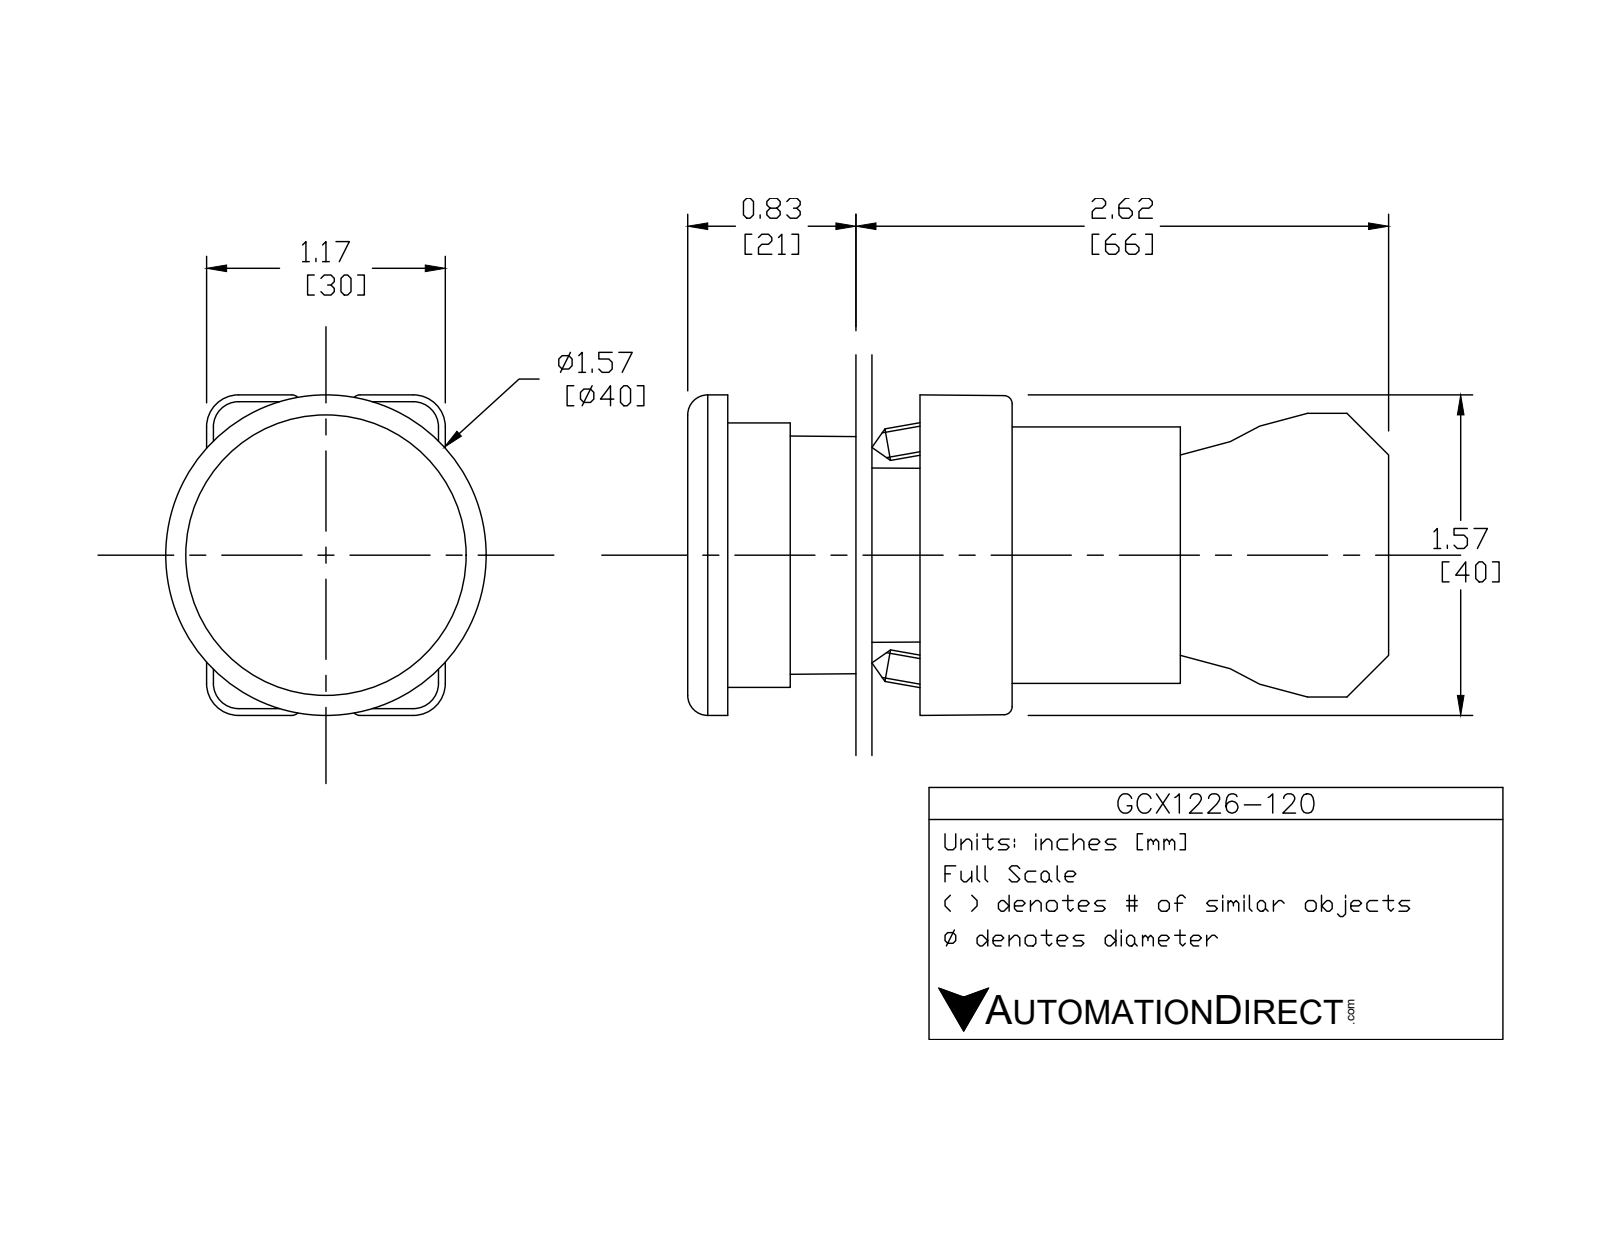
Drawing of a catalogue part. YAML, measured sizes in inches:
part_name: "GCX1226-120; ECX1050; ecx1030; GCX122X OPERATOR (+1 more)"
step_written_by: "SolidWorks 2016 (AUTOMOTIVE_DESIGN)"
units: inches
bodies: {solids: 7, faces: 431, planar: 252, cylindrical: 146, other: 33}
overall_size: [3.469, 1.581, 1.575]
volume: 2.895
surface_area: 40.89
round_holes:
  - {diameter: 0.079, count: 2}
  - {diameter: 0.124, count: 2}
  - {diameter: 0.13, count: 2}
  - {diameter: 0.087, count: 1}
  - {diameter: 0.197, count: 1}
  - {diameter: 0.469, count: 1}
  - {diameter: 0.878, count: 1}
  - {diameter: 0.888, count: 1}
  - {diameter: 1.024, count: 1}
  - {diameter: 1.181, count: 1}
round_bosses_or_shafts:
  - {diameter: 0.157, count: 4}
  - {diameter: 1.299, count: 1}
  - {diameter: 1.175, count: 1}
  - {diameter: 0.945, count: 1}
  - {diameter: 0.856, count: 1}
  - {diameter: 0.78, count: 1}
  - {diameter: 0.504, count: 1}
partial_cylinders:
  - {radius: 0.059, count: 24}
  - {radius: 0.041, count: 12}
  - {radius: 0.124, count: 12}
  - {radius: 0.157, count: 12}
  - {radius: 0.039, count: 8}
  - {radius: 0.128, count: 2}
  - {radius: 0.02, count: 1}
  - {radius: 0.063, count: 1}
face_to_face_distances: [0.827, 2.445, 1.618, 0.579, 2.287, 1.461, 0.157, 0.587, 0.031, 1.165]
hole_center_spacings: [0.236, 0.539, 0.472, 0.484]
